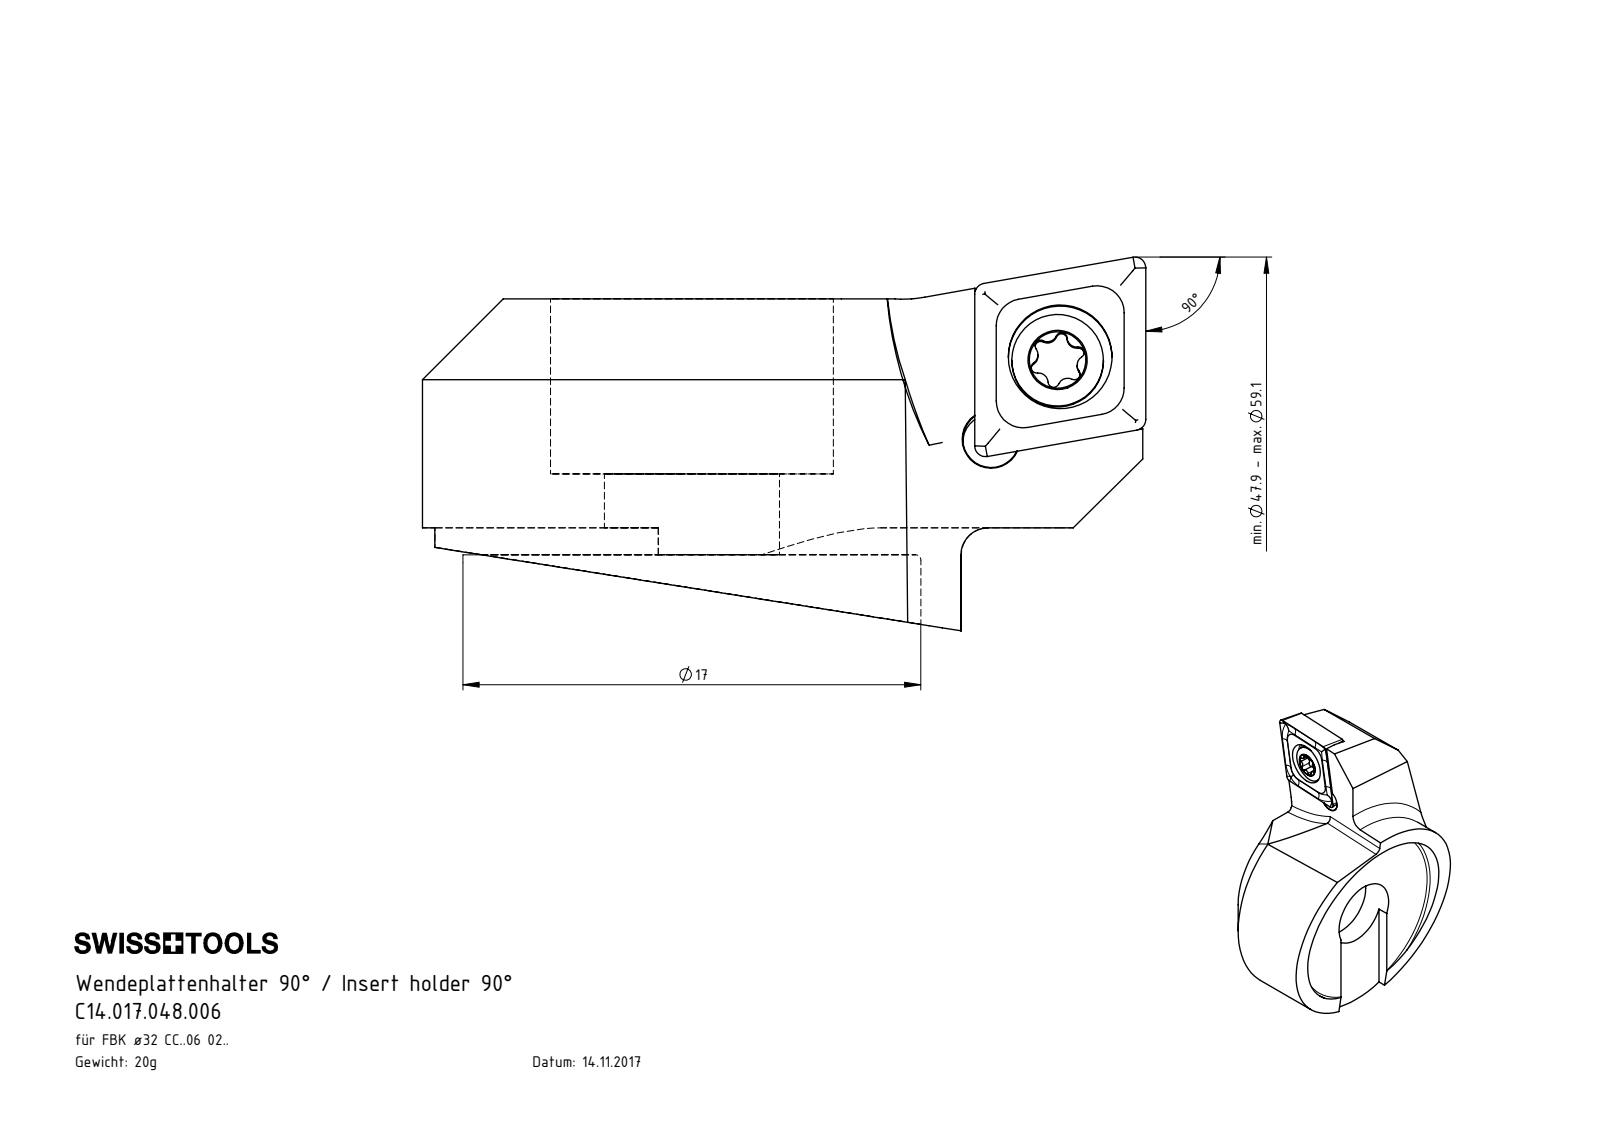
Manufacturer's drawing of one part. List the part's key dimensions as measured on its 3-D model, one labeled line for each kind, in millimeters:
Part name (STEP PRODUCT): F32-WCA.001.011_C_fertigbearbeitet; C14.017.048.006; WCA-ER2.001.006_A; CCMT060204
STEP written by: SolidWorks 2017 (CONFIG_CONTROL_DESIGN)
Units: millimetres
Bodies: 3 solids, 134 faces (38 planar, 42 cylindrical, 54 other)
Overall size (bounding box): 26.85 × 20 × 13.87
Volume: 2 542 mm³ · Surface area: 1 915 mm²
Round holes (diameter × count): ⌀2.05 ×1, ⌀2.1 ×1, ⌀2.8 ×1, ⌀3.85 ×1, ⌀6.5 ×1, ⌀10.5 ×1
Round bosses / shafts (diameter × count): ⌀20 ×1, ⌀3.4 ×1, ⌀2.5 ×1
Partial cylindrical surfaces — rounded edges, fillets, slot ends (radius × count): R0.21 ×6, R0.36 ×5, R0.5 ×2, R0.36 ×1, R5 ×1, R8.5 ×1, R15 ×1
Main face-to-face distances: 1, 8.5, 9.5, 6.5, 2, 3, 2.28, 2.27, 2.38, 2.39
Hole centre spacings: 3.84, 3.99
